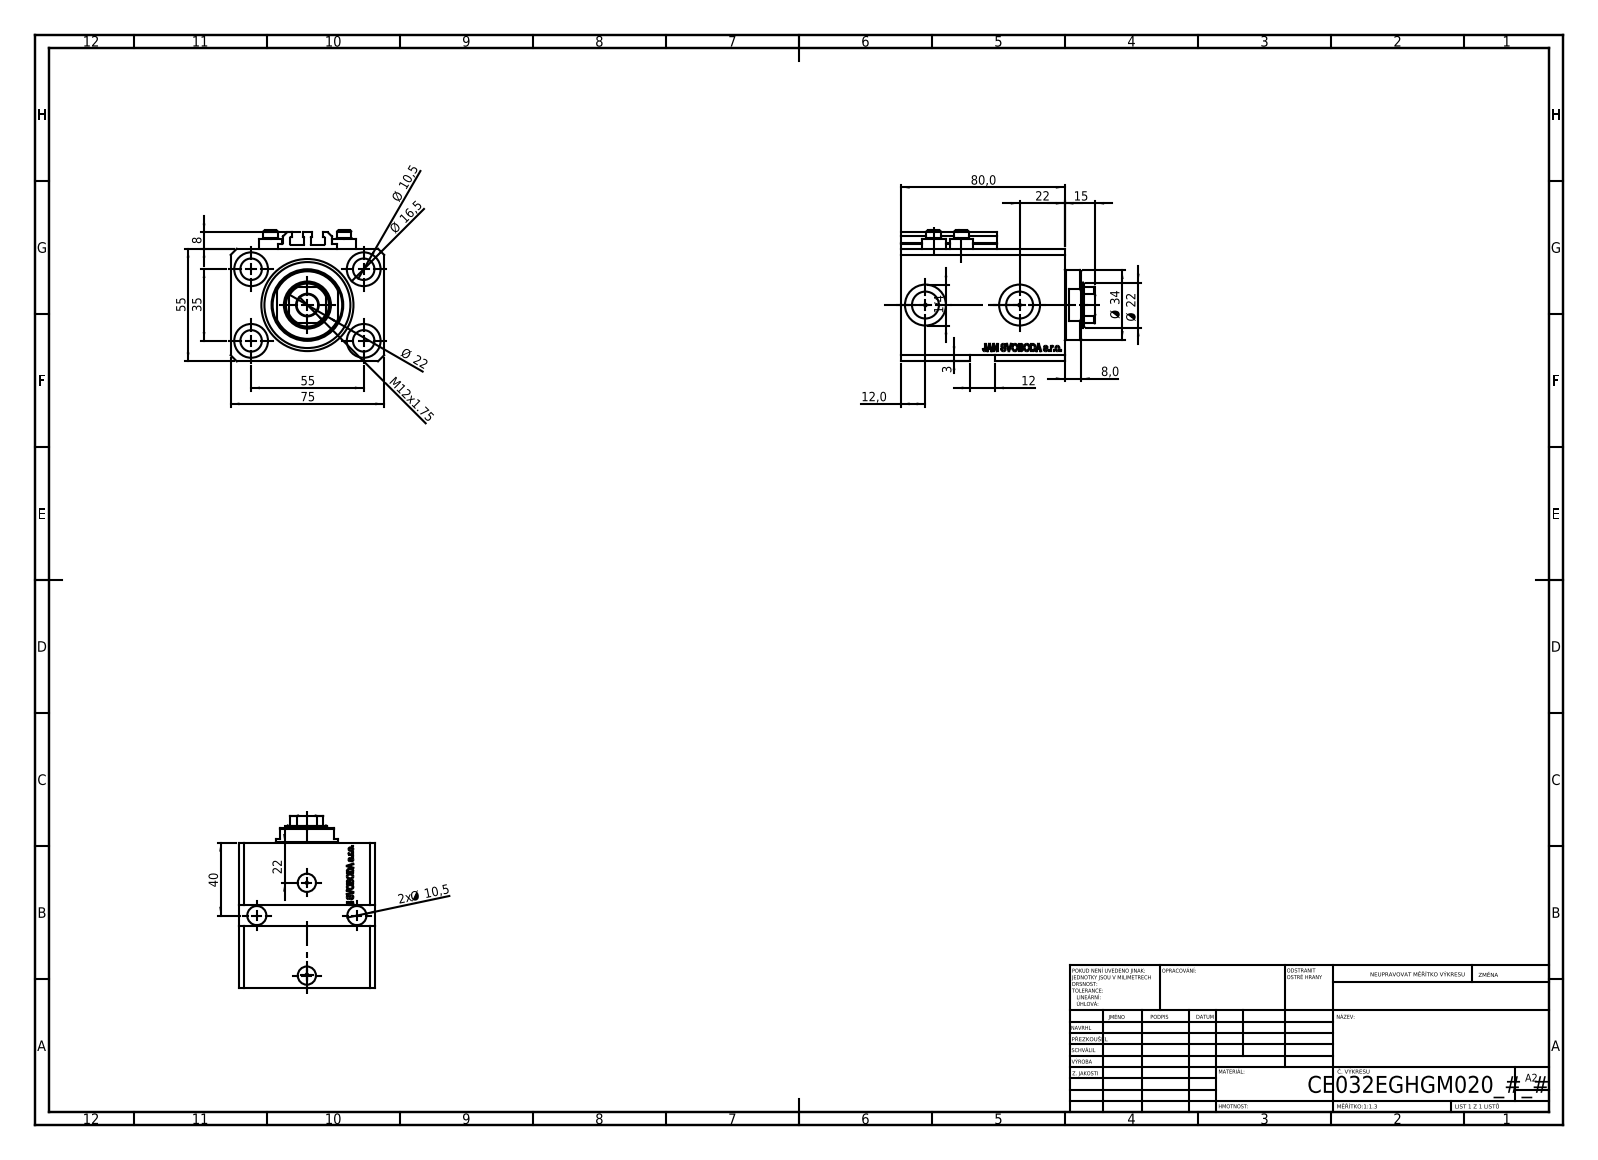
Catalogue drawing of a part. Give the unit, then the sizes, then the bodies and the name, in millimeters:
Units: millimetres
Overall size (bounding box): 95 × 75 × 64
Round holes (diameter × count): ⌀10.5 ×7, ⌀1.25 ×4, ⌀4 ×4, ⌀16.5 ×4, ⌀10 ×2, ⌀13.16 ×2, ⌀20 ×2, ⌀22 ×1, ⌀32 ×1, ⌀45 ×1
Round bosses / shafts (diameter × count): ⌀11.6 ×4, ⌀7 ×4, ⌀34 ×1
Partial cylindrical surfaces — rounded edges, fillets, slot ends (radius × count): R0.2 ×10, R10.5 ×1
Main face-to-face distances: 55, 75, 15, 80, 65, 3, 55.1, 9.9, 70.1, 54
Hole centre spacings: 32.6, 55, 13.6, 14.09, 19.89, 20.12, 25.81, 28.48
Volume: 283 894 mm³ · Surface area: 74 463 mm²
Bodies: 8 solids, 1064 faces (514 planar, 126 cylindrical, 424 other)
Part name (STEP PRODUCT): V250CE_VC_E; V250CE_C_VCP; V250CE_E_Body; ALLEN BOLT V250CE
STEP written by: SolidWorks 2019 (CONFIG_CONTROL_DESIGN)
